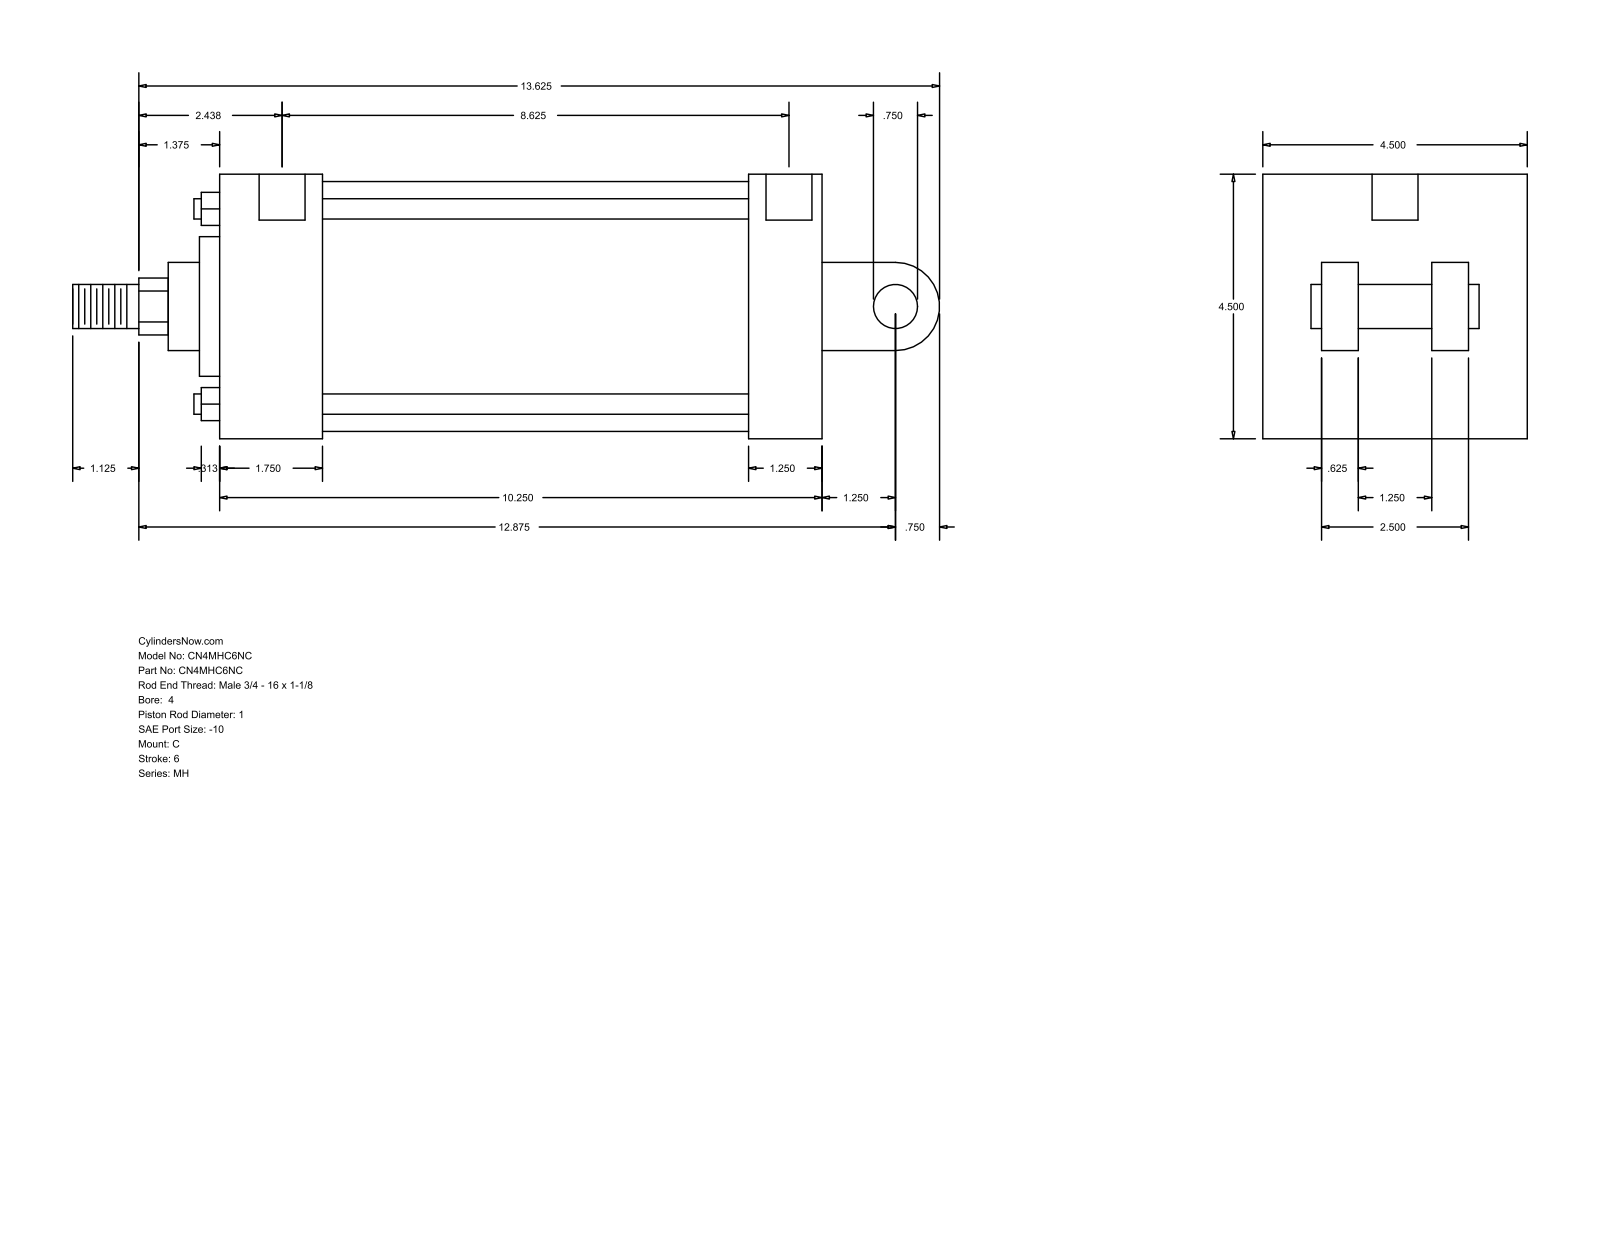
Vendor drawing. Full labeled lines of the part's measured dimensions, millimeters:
Part name (STEP PRODUCT): MH_C__0400_1
STEP written by: GSSL Pune (CONFIG_CONTROL_DESIGN)
Units: millimetres
Bodies: 0 solids, 101 faces (71 planar, 30 cylindrical, 0 other)
Overall size (bounding box): 374.65 × 114.3 × 114.3
Round holes (diameter × count): ⌀8.73 ×4, ⌀19.84 ×2
Round bosses / shafts (diameter × count): ⌀8.76 ×4, ⌀19.05 ×2, ⌀107.95 ×1, ⌀60.33 ×1, ⌀38.1 ×1, ⌀25.4 ×1
Partial cylindrical surfaces — rounded edges, fillets, slot ends (radius × count): R12.29 ×1, R19.05 ×1
Main face-to-face distances: 114.3, 260.35, 44.46, 228.6, 184.14, 215.89, 31.75, 73.03, 41.27, 38.1
Hole centre spacings: 1.58, 220.66, 222.24, 219.08
